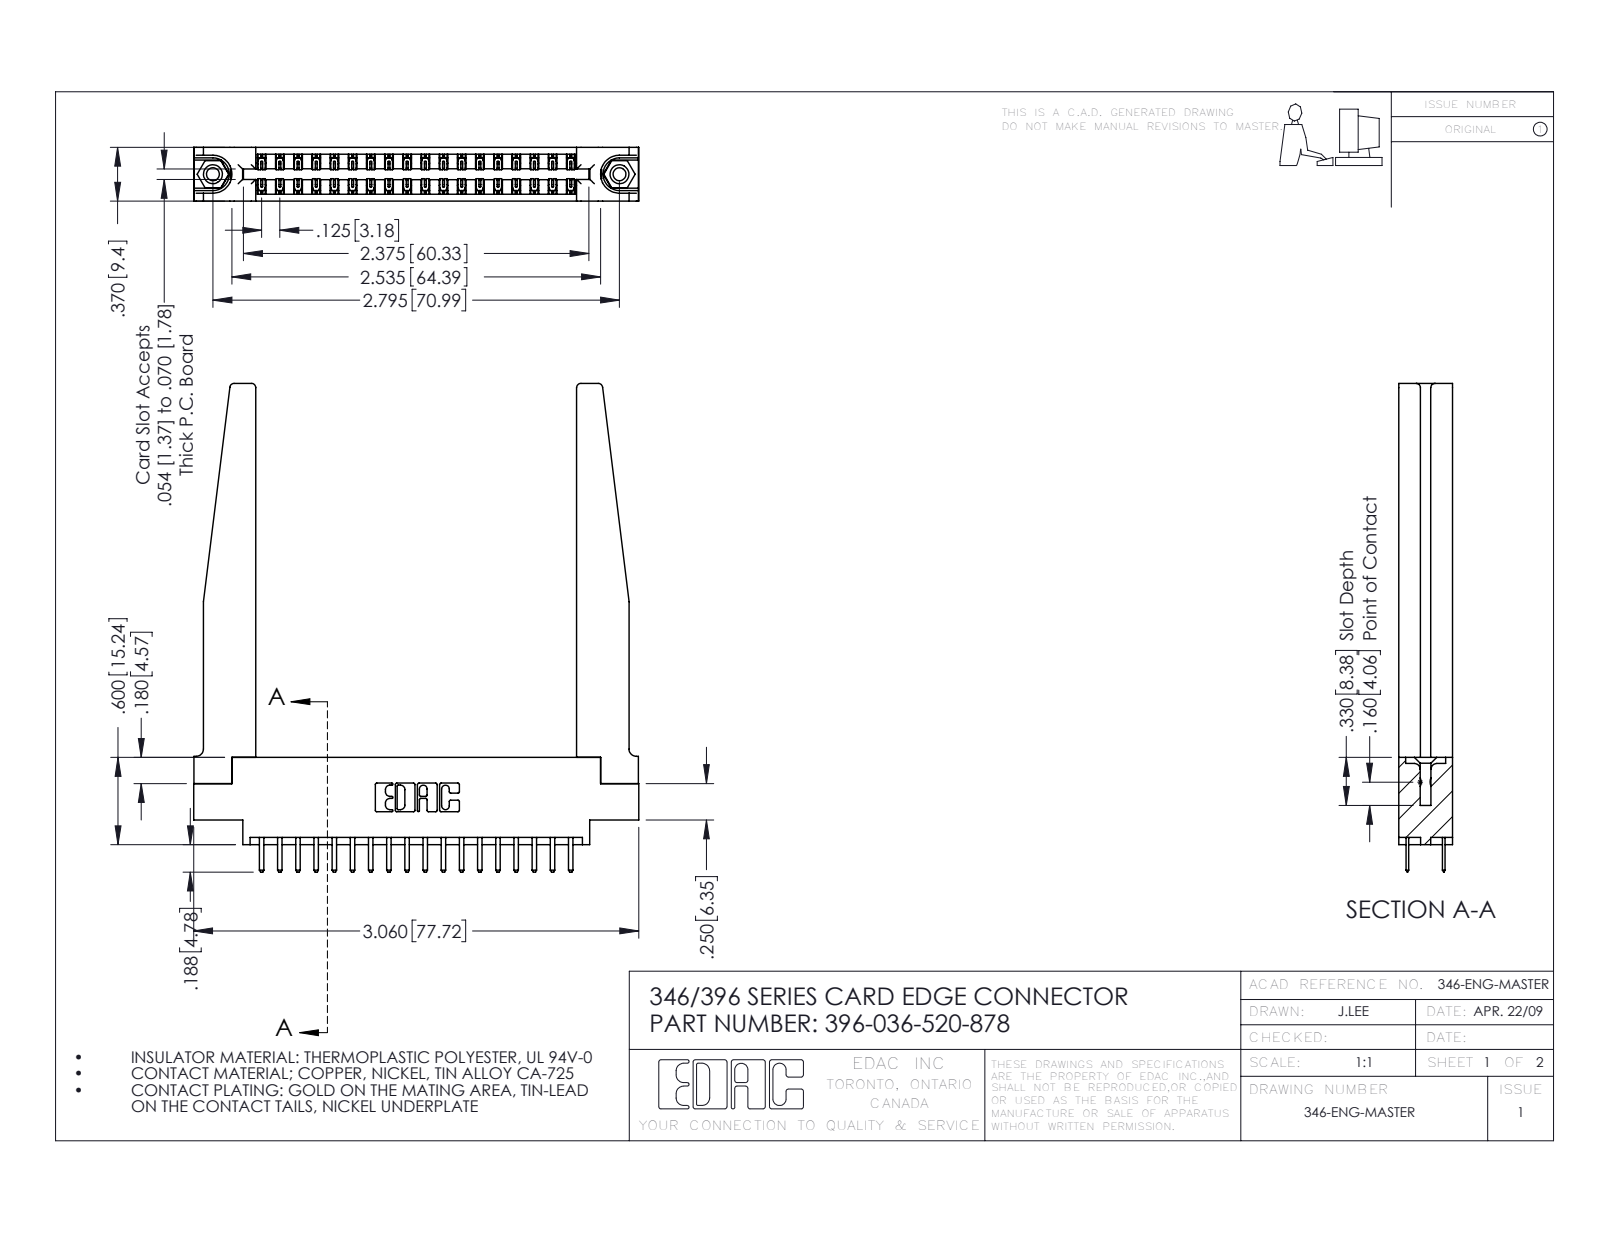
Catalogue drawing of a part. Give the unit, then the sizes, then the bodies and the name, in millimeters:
Units: millimetres
Overall size (bounding box): 85.3 × 77.7 × 9.4
Round holes (diameter × count): ⌀2.3 ×2, ⌀3.2 ×2, ⌀4 ×2, ⌀1.6 ×1
Round bosses / shafts (diameter × count): ⌀3.9 ×2
Partial cylindrical surfaces — rounded edges, fillets, slot ends (radius × count): R0.2 ×54, R0.3 ×40, R0.3 ×22, R0.8 ×8, R0.2 ×6, R0.8 ×6, R0.7 ×3, R0.4 ×2
Main face-to-face distances: 9.4, 3.8, 1.2, 8.2, 1.8, 3.8, 6.4, 2.6, 5.6, 4.4
Hole centre spacings: 6.2, 65.7, 71
Volume: 14 100 mm³ · Surface area: 16 230 mm²
Bodies: 41 solids, 2376 faces (1554 planar, 770 cylindrical, 52 other)
Part name (STEP PRODUCT): 346 Part_0.170 Offset - 0.156 Dia-TH; 345-292-001_345-293-120; 396-036-520-878; 345-250-001_345-250-001-102 (+1 more)
STEP written by: SolidWorks 2016 (CONFIG_CONTROL_DESIGN)
